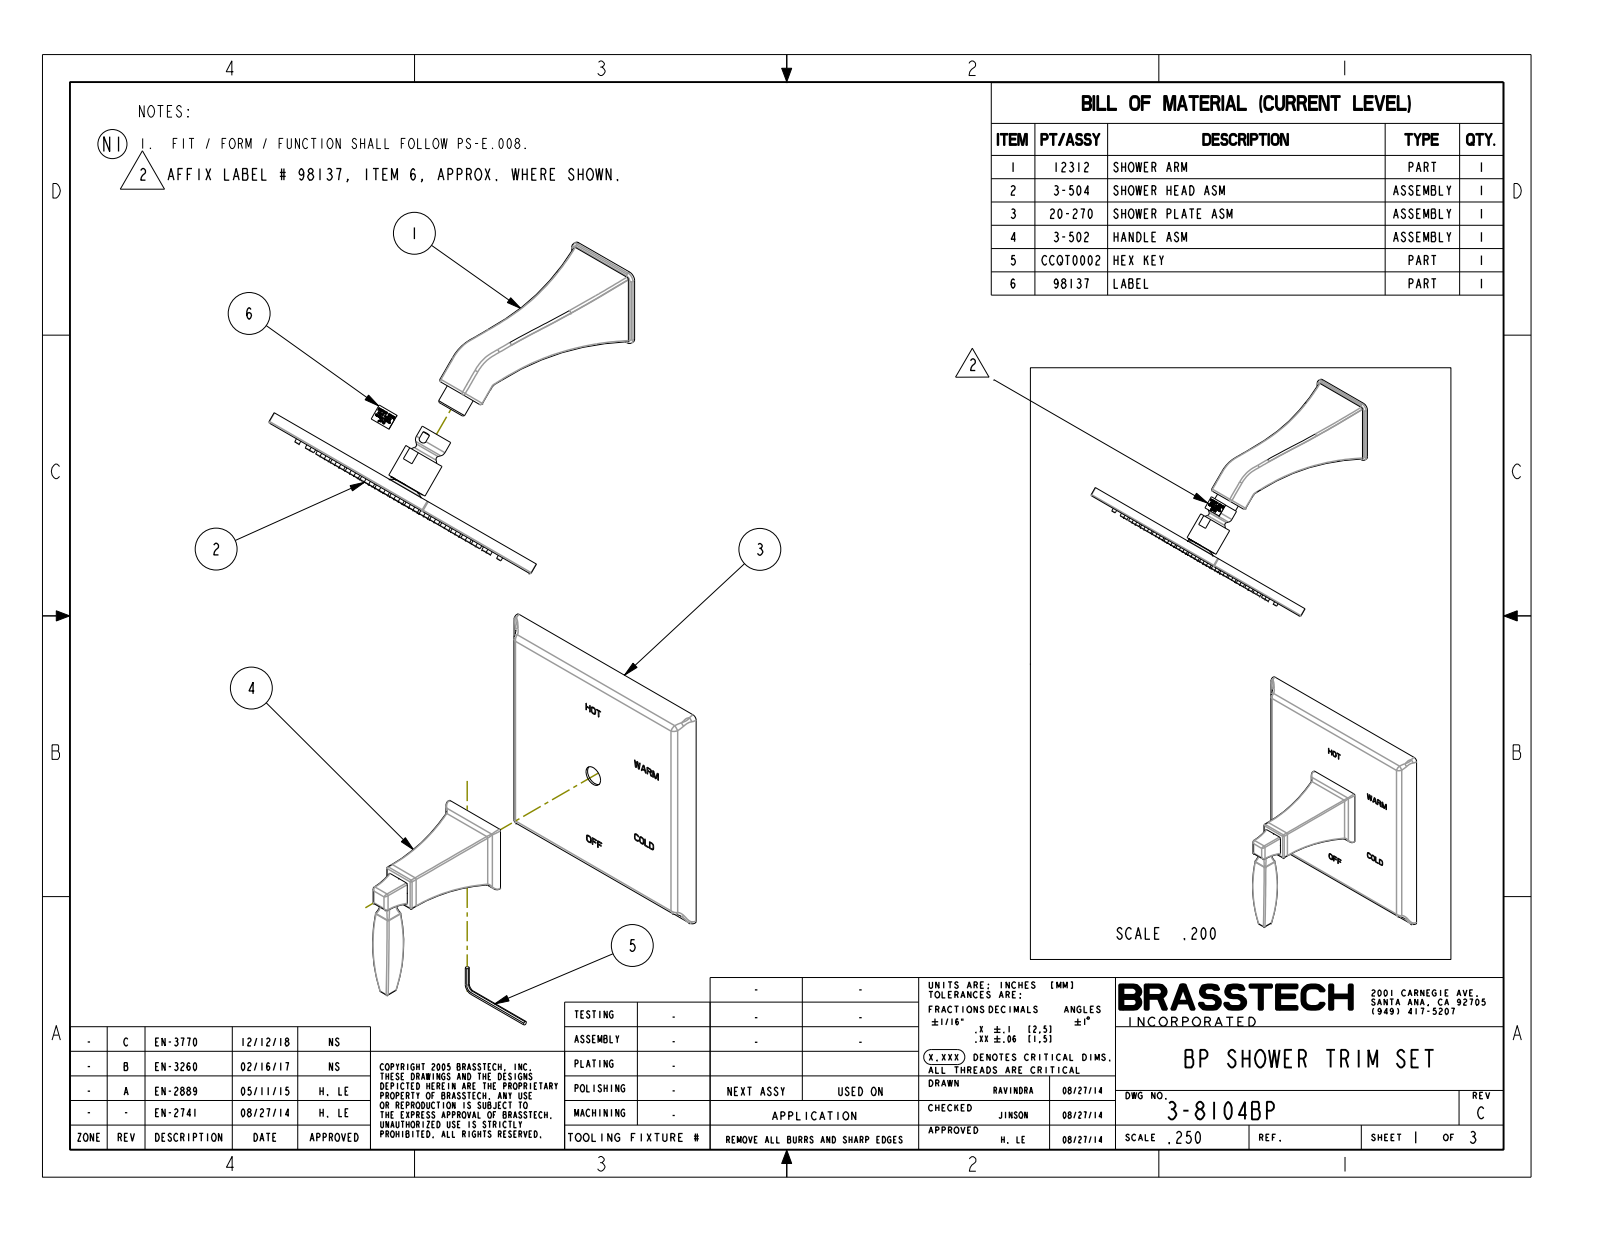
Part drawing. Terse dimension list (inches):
name: 12312; ATBE0165-01_1; MANIFOLD_SOLID_BREP_48721_1; CTMBXXXX_1_1 (+8 more)
written by: PRO/ENGINEER BY PARAMETRIC TECHNOLOGY CORPORATION, 2013150 (CONFIG_CONTROL_DESIGN)
unit: in
bodies: 18 solids, 1817 faces (771 planar, 520 cylindrical, 526 other)
size: 20.67 × 9.233 × 7
volume: 24.2 in³; area: 419.9 in²
holes: 2× ⌀0.945, 1× ⌀0.13, 1× ⌀0.156, 1× ⌀0.165, 1× ⌀0.197, 1× ⌀0.288, 1× ⌀0.335, 1× ⌀0.394, 1× ⌀0.447, 1× ⌀0.512, 1× ⌀0.531, 1× ⌀0.563
bosses: 2× ⌀1.339, 1× ⌀1.11, 1× ⌀1.043, 1× ⌀0.866, 1× ⌀0.823, 1× ⌀0.748, 1× ⌀0.728, 1× ⌀0.63
rounds: 100× R0.008, 34× R0.039, 30× R0.004, 15× R0.015, 8× R0.079, 6× R0.188, 4× R0.062, 4× R0.098
face distances: 0.059, 0.315, 0.256, 0.197, 0.5, 0.441, 0.244, 5.945, 6.26, 5.63
hole spacings: 16
